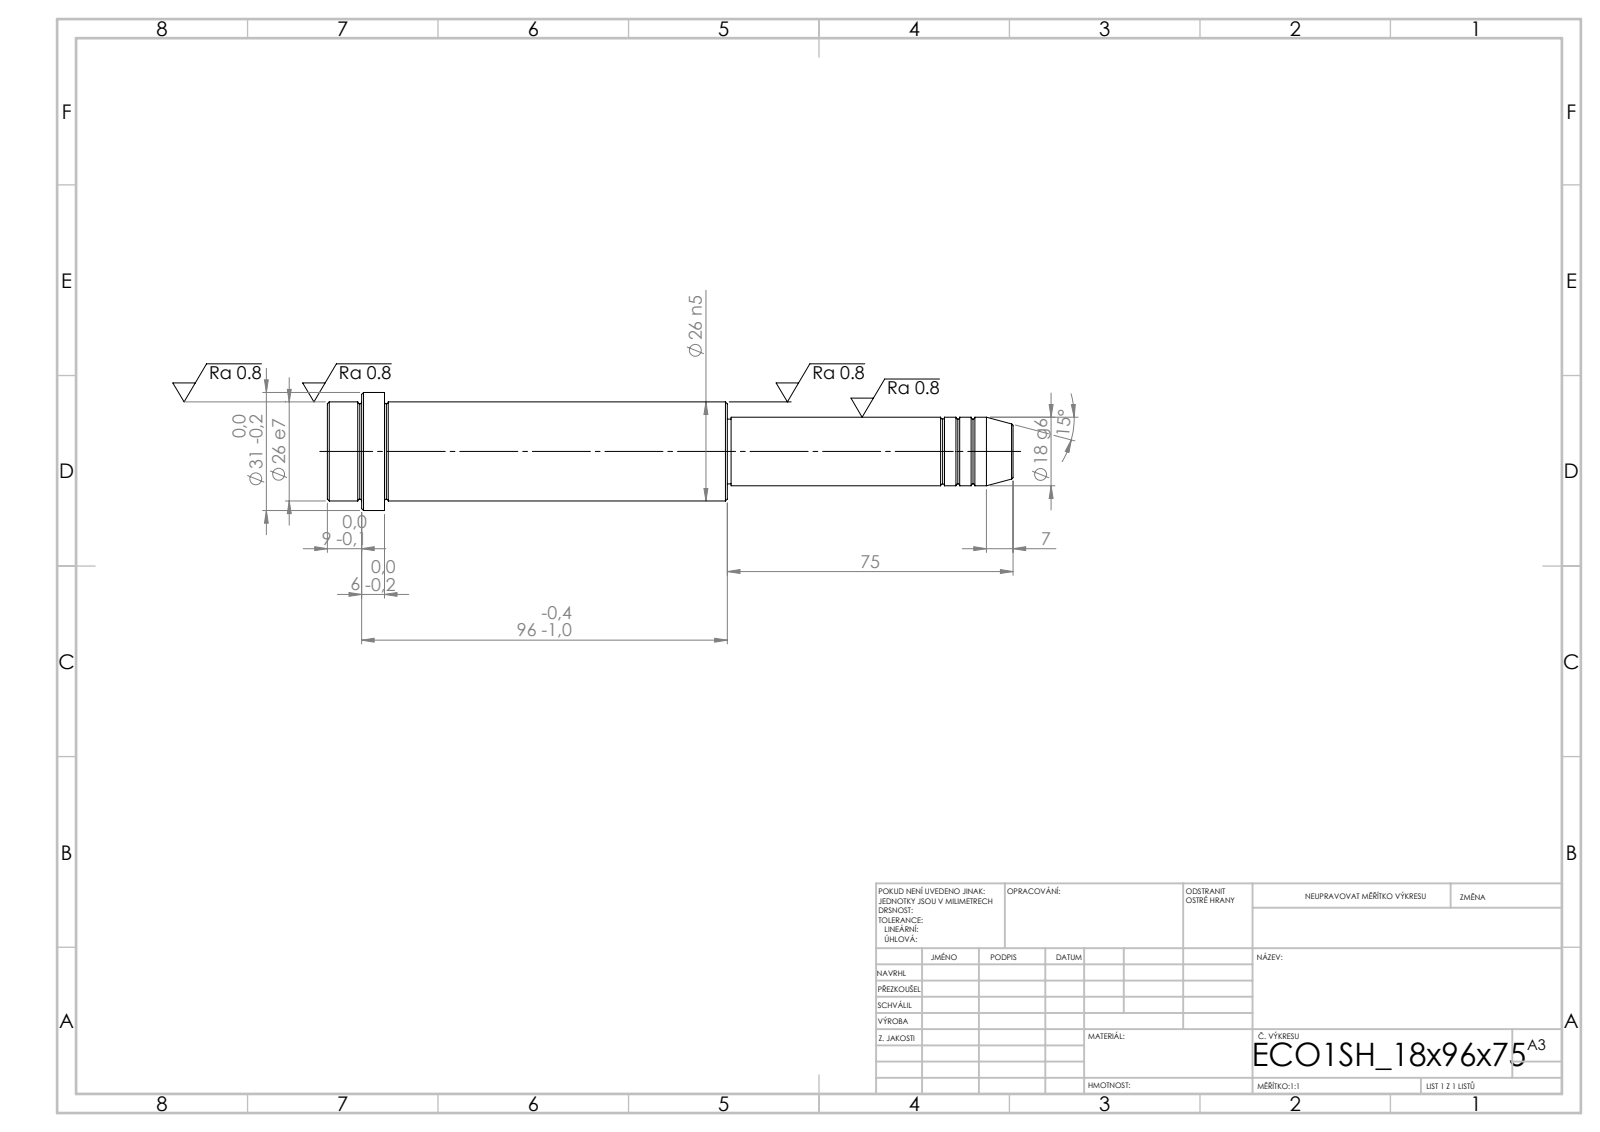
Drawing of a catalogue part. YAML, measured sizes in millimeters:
step_written_by: "SolidWorks 2019 (CONFIG_CONTROL_DESIGN)"
units: millimeters
bodies: {solids: 1, faces: 52, planar: 6, cylindrical: 16, other: 30}
overall_size: [180, 31, 31]
volume: 75641
surface_area: 14441
round_bosses_or_shafts:
  - {diameter: 31, count: 1}
  - {diameter: 26, count: 1}
  - {diameter: 18, count: 1}
  - {diameter: 17, count: 1}
face_to_face_distances: [105, 90, 15, 96, 6, 9, 75, 165, 171, 180]
